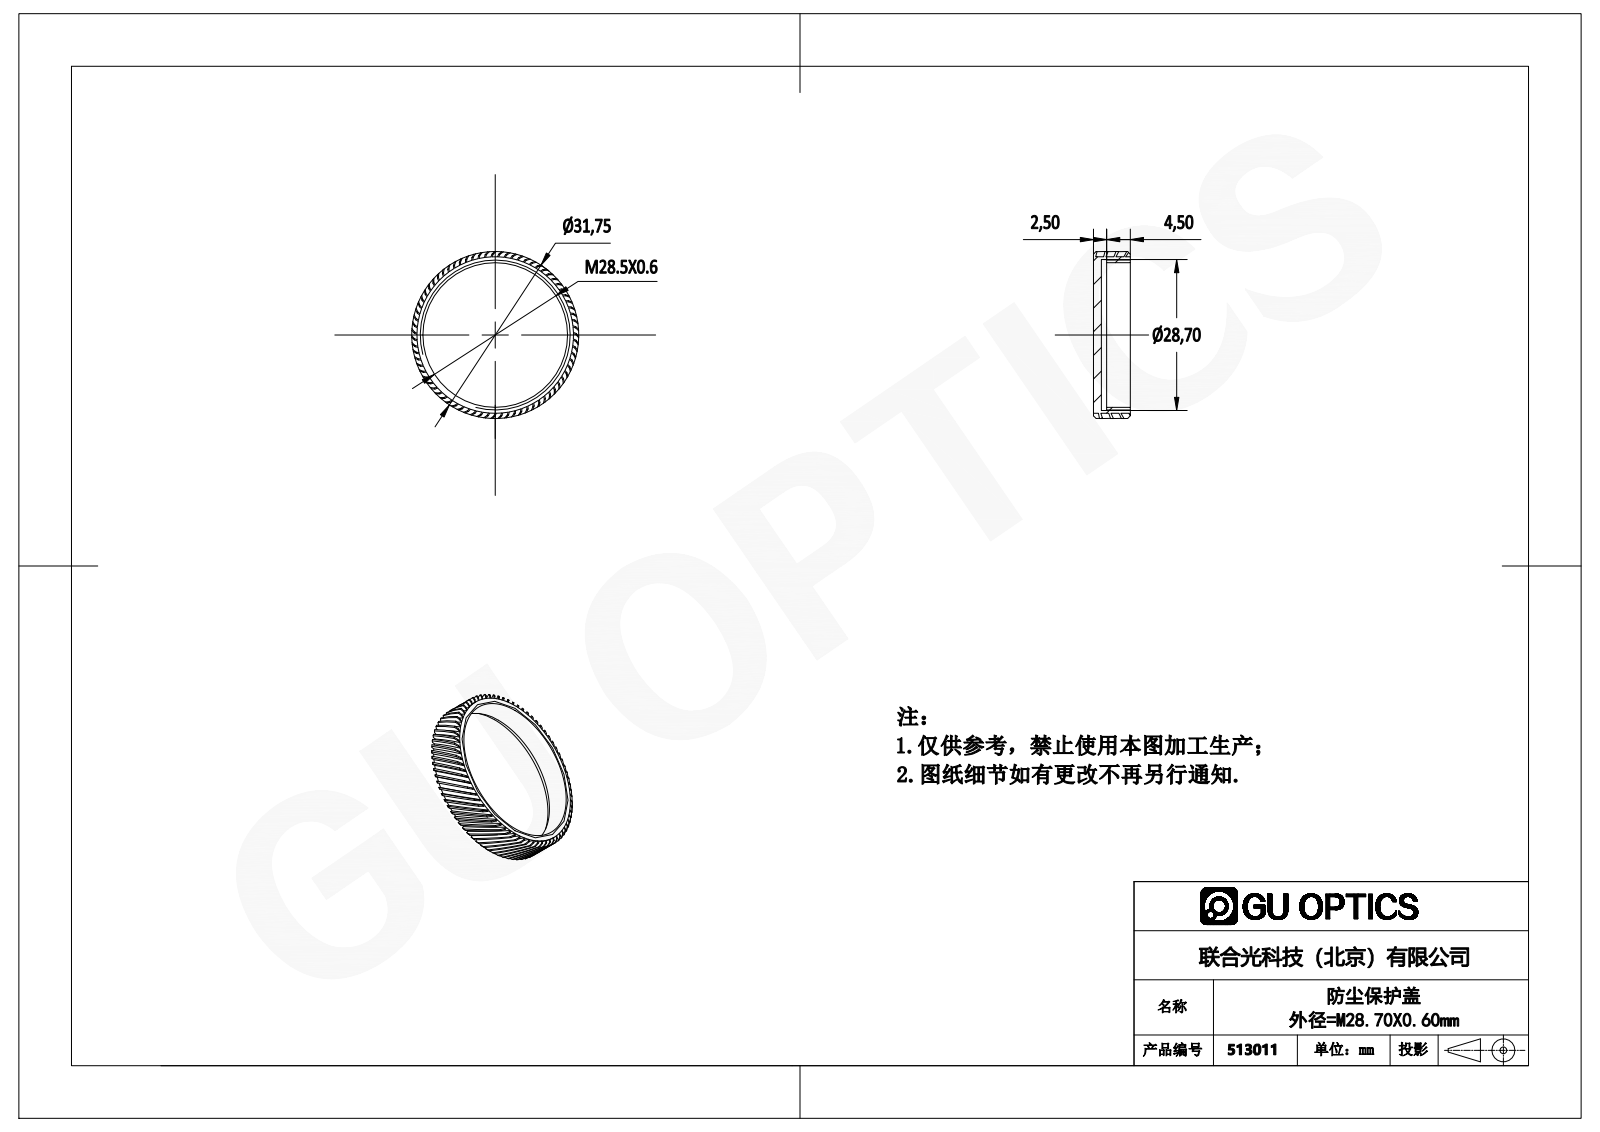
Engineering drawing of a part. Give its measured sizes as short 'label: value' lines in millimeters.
name: 513011
written by: SolidWorks 2016 (AUTOMOTIVE_DESIGN)
unit: mm
bodies: 1 solid, 463 faces (154 planar, 158 cylindrical, 151 other)
size: 31.75 × 31.75 × 7
volume: 1 702 mm³; area: 3 946 mm²
holes: 1× ⌀27.5, 1× ⌀28.7
bosses: 1× ⌀31.75, 1× ⌀29.75
face distances: 1.5, 0.8, 5.5, 7, 4.5, 1, 2.5, 0.79, 0.81
